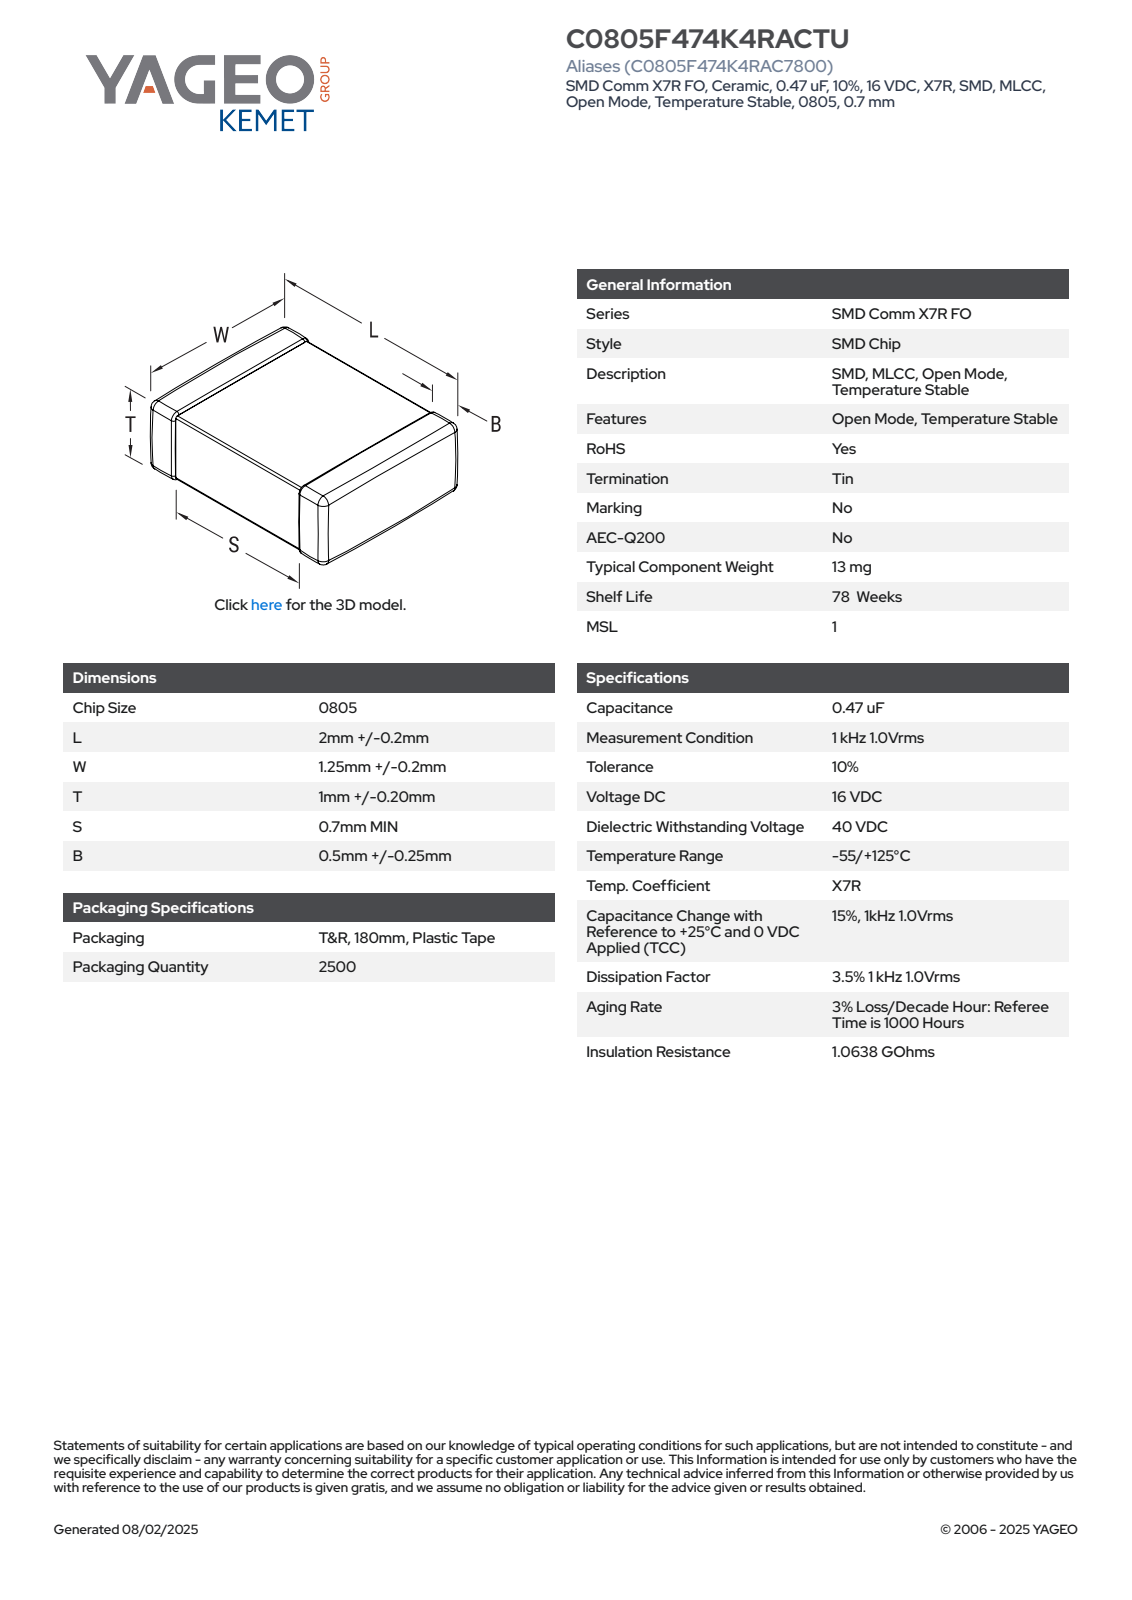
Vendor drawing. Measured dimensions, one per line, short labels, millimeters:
name: CCS_CCSTD_0805_L2.2W1.45T1.2B0.5
written by: SolidWorks 2014 (AUTOMOTIVE_DESIGN)
unit: mm
bodies: 4 solids, 125 faces (71 planar, 38 cylindrical, 16 other)
size: 2.2 × 1.45 × 1.2
volume: 4 mm³; area: 15 mm²
face distances: 1.17, 1.42, 1.14, 2.2, 1.39, 1.2, 1.45, 0.97, 1.23, 1.19
